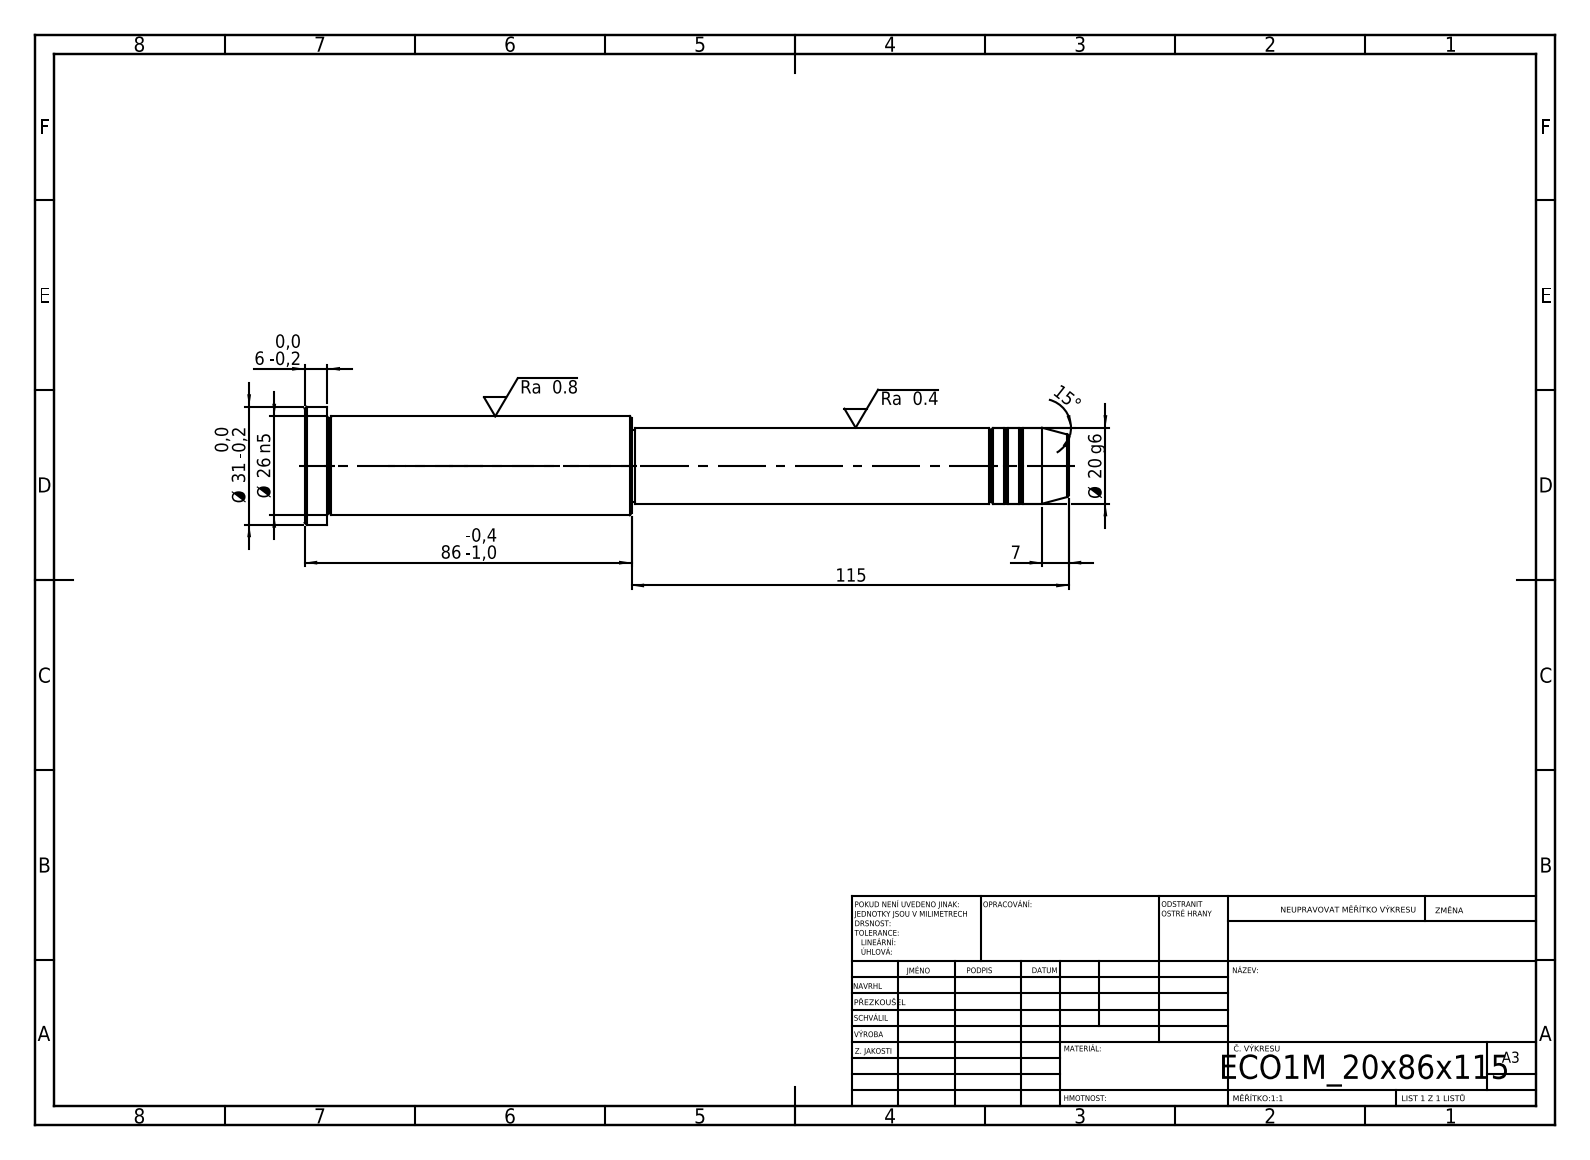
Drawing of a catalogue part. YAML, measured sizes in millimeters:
step_written_by: "SolidWorks 2019 (CONFIG_CONTROL_DESIGN)"
units: millimeters
bodies: {solids: 1, faces: 43, planar: 5, cylindrical: 14, other: 24}
overall_size: [201, 31, 31]
volume: 82586
surface_area: 15861
round_bosses_or_shafts:
  - {diameter: 31, count: 1}
  - {diameter: 26, count: 1}
  - {diameter: 20, count: 1}
  - {diameter: 19, count: 1}
face_to_face_distances: [6, 80, 86, 115, 195, 201, 114, 1, 81, 87]
